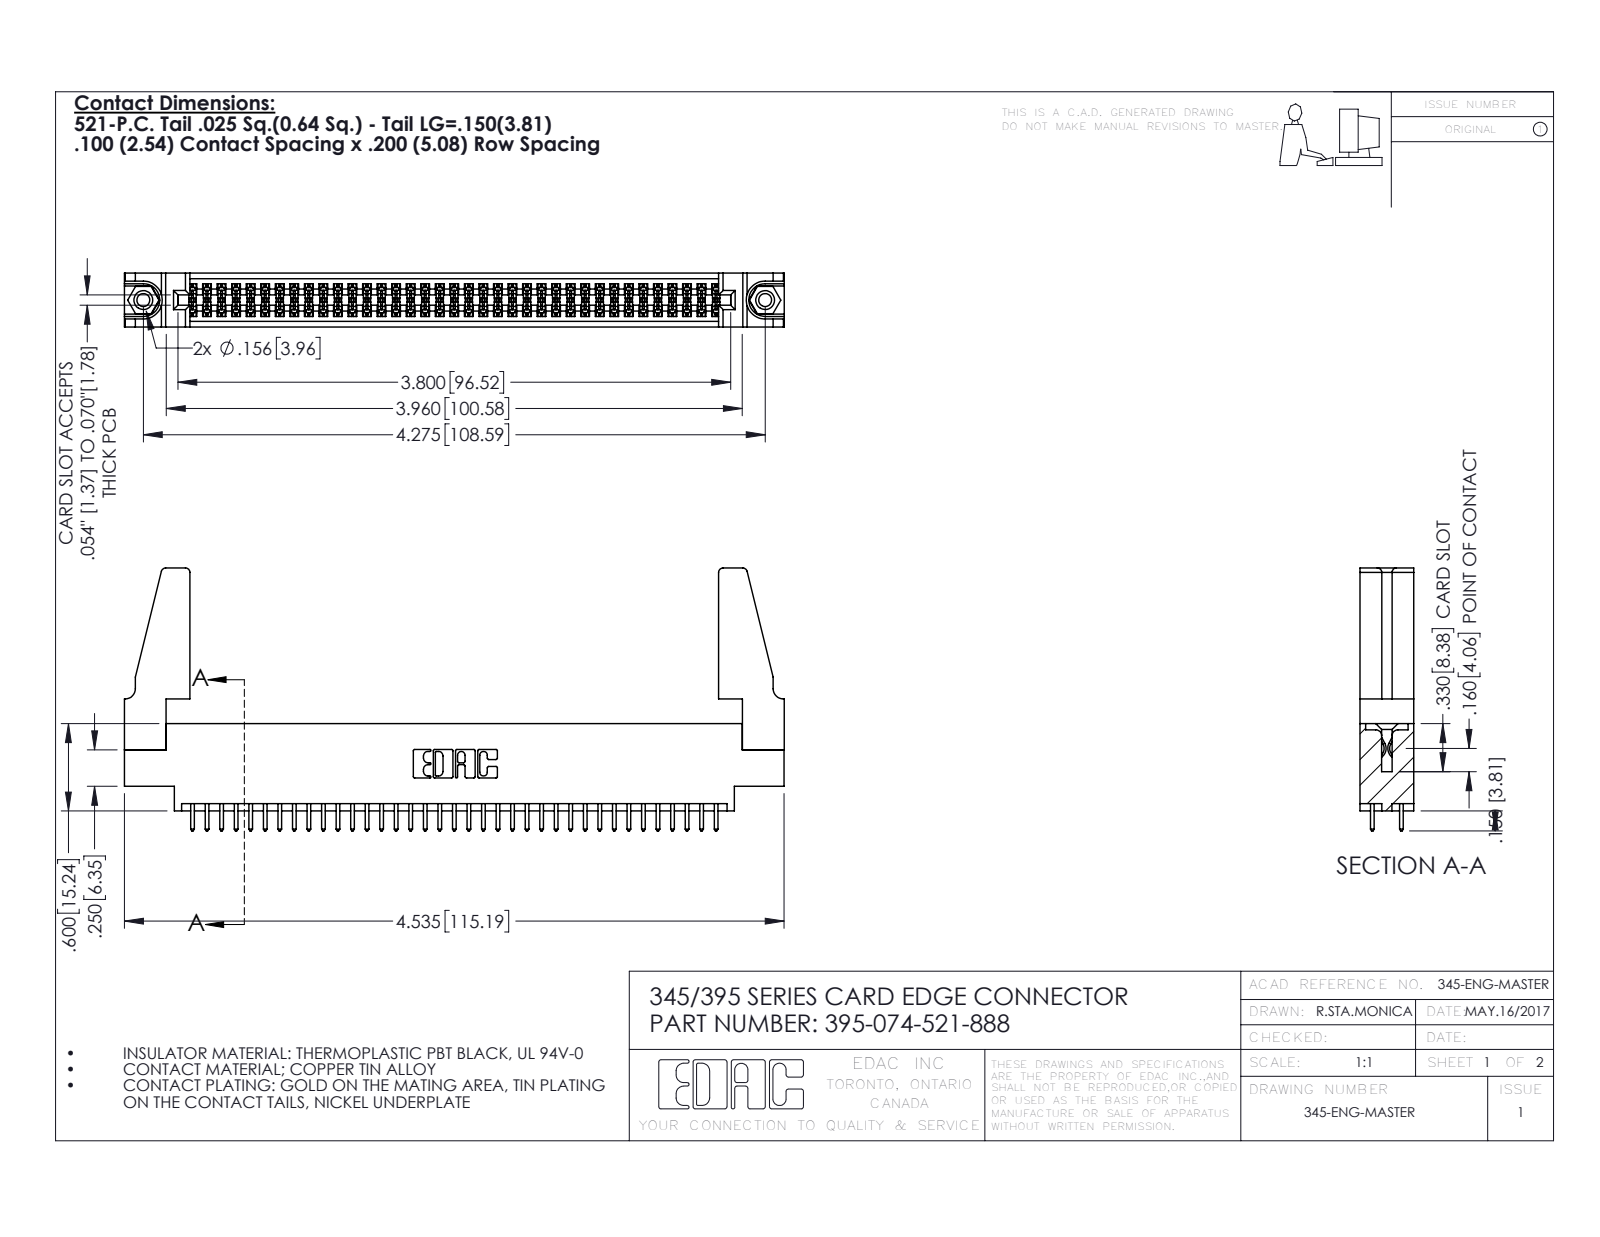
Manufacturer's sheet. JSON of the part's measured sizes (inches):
{"part_name": "395-074-521-888; 345-292-001_345-293-121; 345 Part_0.170 Offset - 0.156 Dia-TH; 345-220-078_345-220-088 (+1 more)", "step_written_by": "SolidWorks 2016 (CONFIG_CONTROL_DESIGN)", "units": "inches", "bodies": {"solids": 79, "faces": 3954, "planar": 2598, "cylindrical": 1340, "other": 16}, "overall_size": [4.536, 1.807, 0.37], "volume_in3": 0.87, "surface_area_in2": 29.81, "round_holes": [[0.089, 2], [0.125, 2], [0.156, 2], [0.064, 1]], "round_bosses_or_shafts": [[0.155, 2]], "partial_cylinders_radius": [[0.006, 111], [0.01, 74], [0.01, 22], [0.03, 8], [0.007, 6], [0.031, 6], [0.026, 3], [0.014, 2]], "face_to_face_distances": [0.072, 0.298, 0.37, 0.098, 0.272, 0.025, 0.2, 0.225, 0.175, 0.149], "hole_center_spacings": [0.27, 4.039, 4.275]}
